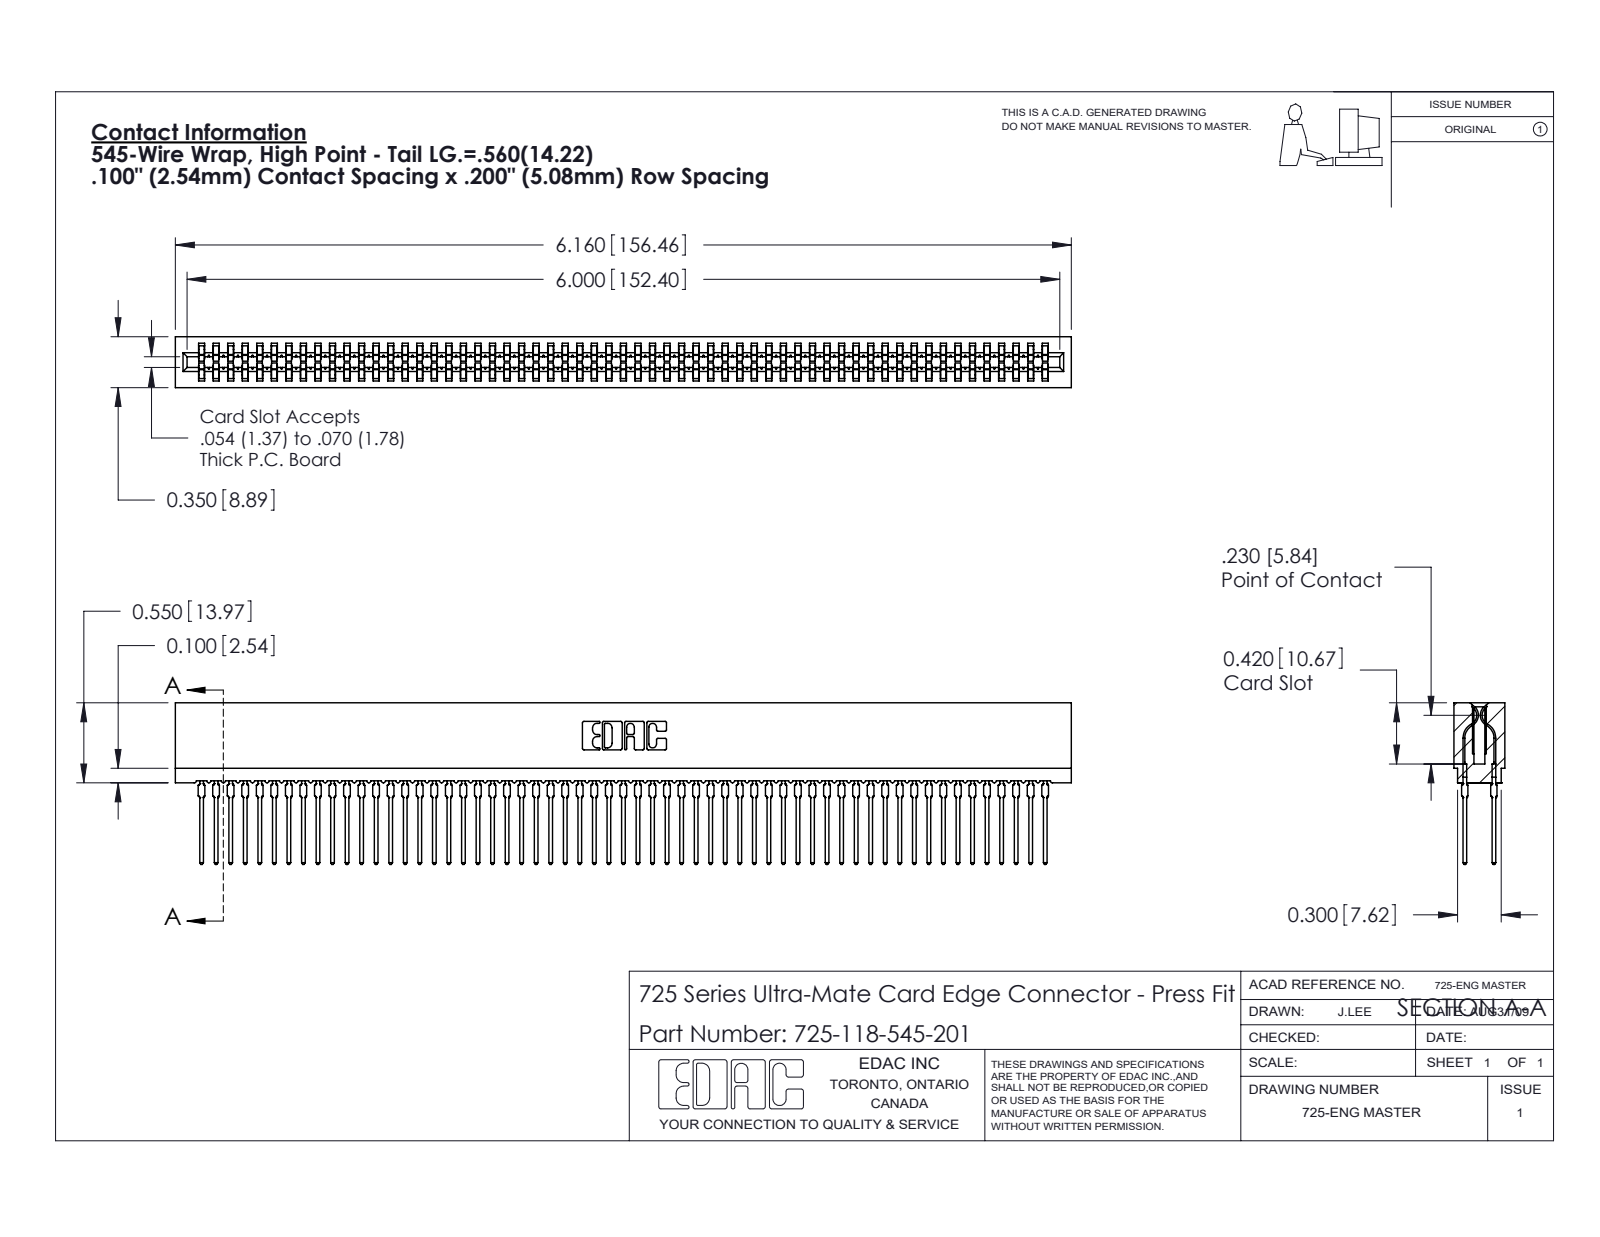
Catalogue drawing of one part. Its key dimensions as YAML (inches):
part_name: "725-118-545-201; 745-292-001_545; 725 Part_Insulator Option - 01"
step_written_by: "SolidWorks 2020 (CONFIG_CONTROL_DESIGN)"
units: inches
bodies: {solids: 119, faces: 10656, planar: 5483, cylindrical: 2105, other: 3068}
overall_size: [6.16, 1.111, 0.35]
volume: 0.777
surface_area: 45.06
partial_cylinders:
  - {radius: 0.021, count: 236}
  - {radius: 0.015, count: 118}
  - {radius: 0.01, count: 22}
  - {radius: 0.005, count: 8}
  - {radius: 0.011, count: 8}
  - {radius: 0.007, count: 6}
  - {radius: 0.031, count: 6}
  - {radius: 0.026, count: 3}
face_to_face_distances: [0.063, 0.287, 0.2, 0.35, 0.212, 0.138, 0.076, 0.149, 0.087, 0.263]
